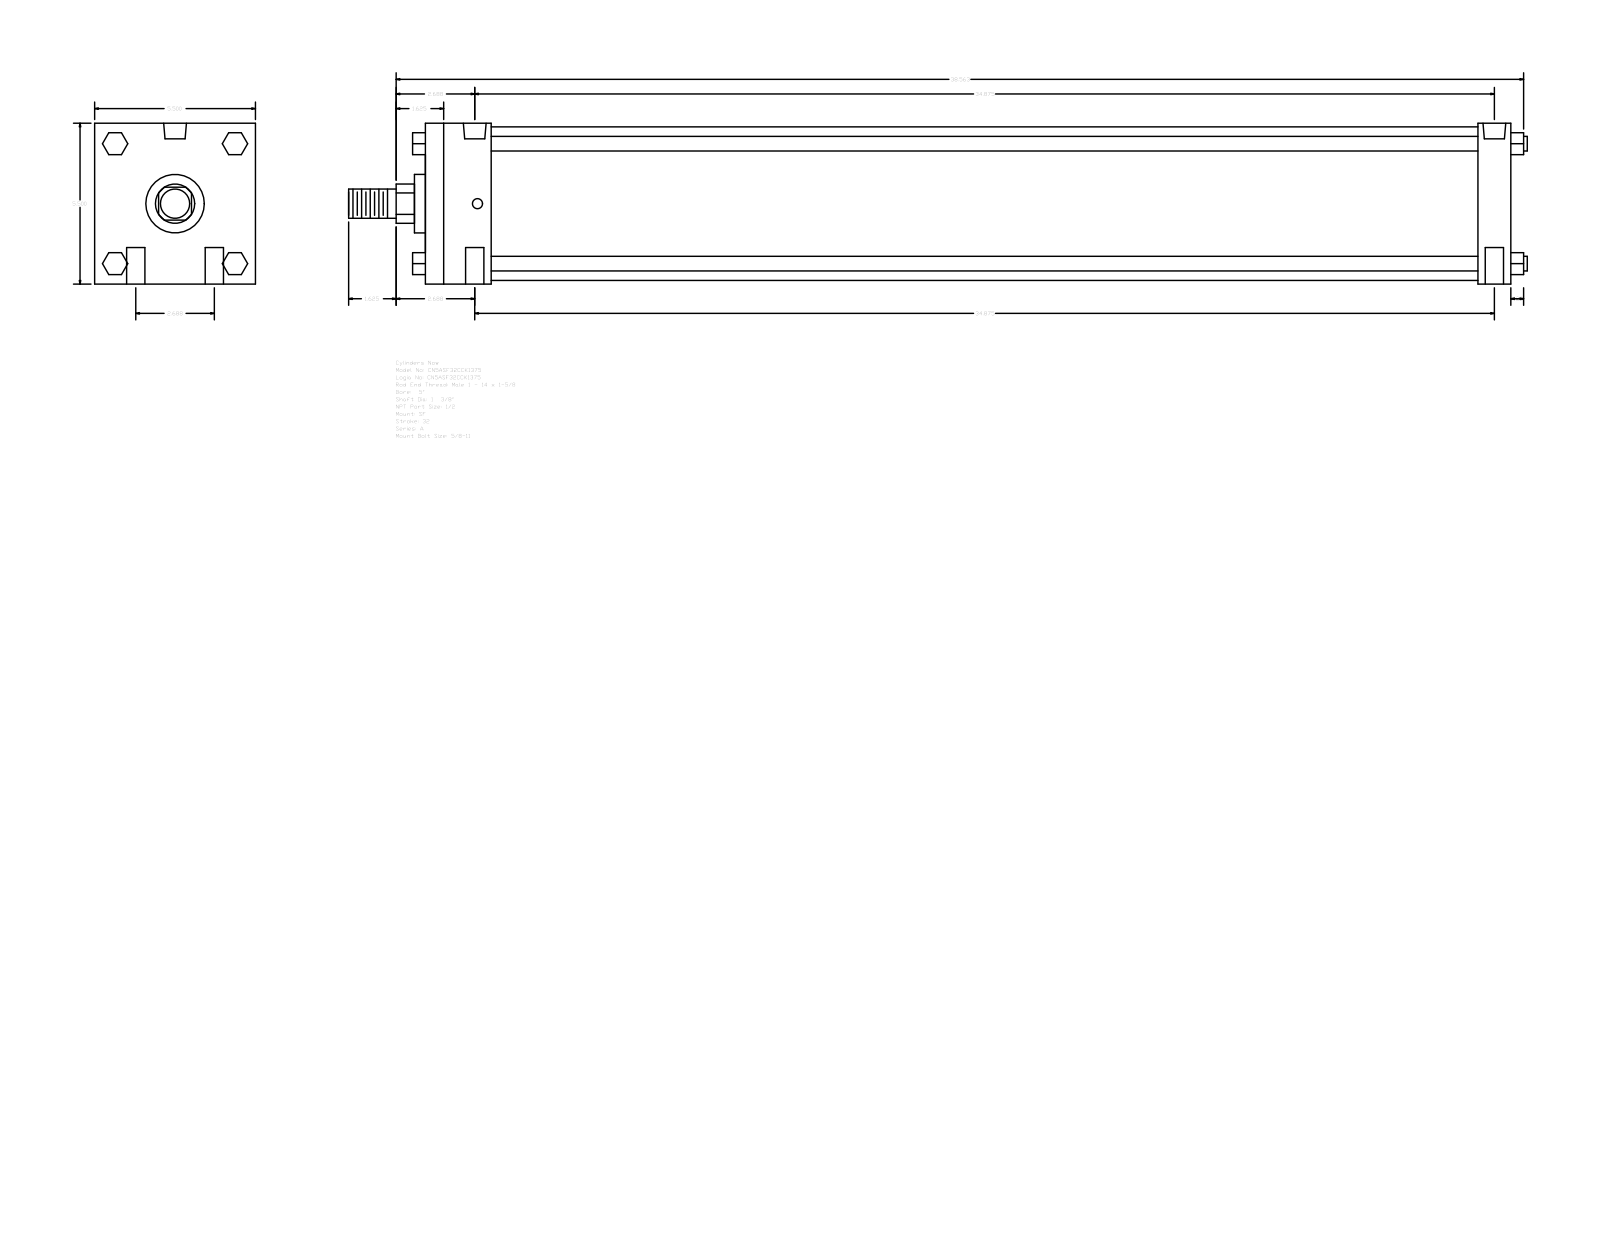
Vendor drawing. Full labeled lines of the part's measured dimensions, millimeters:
Part name (STEP PRODUCT): A_SF__0500_1.375
STEP written by: GSSL Pune (CONFIG_CONTROL_DESIGN)
Units: millimetres
Bodies: 0 solids, 124 faces (94 planar, 30 cylindrical, 0 other)
Overall size (bounding box): 1023.94 × 139.7 × 139.7
Round holes (diameter × count): ⌀15.88 ×4, ⌀8.73 ×2, ⌀19.77 ×2
Round bosses / shafts (diameter × count): ⌀12.7 ×4, ⌀133.35 ×1, ⌀50.8 ×1, ⌀34.92 ×1, ⌀25.4 ×1
Partial cylindrical surfaces — rounded edges, fillets, slot ends (radius × count): R17.06 ×1
Main face-to-face distances: 139.7, 942.98, 57.15, 28.58, 914.4, 857.25, 885.83, 19.05, 52.07, 90.18
Hole centre spacings: 34.13, 886.49, 885.83, 68.26, 888.46, 881.05
